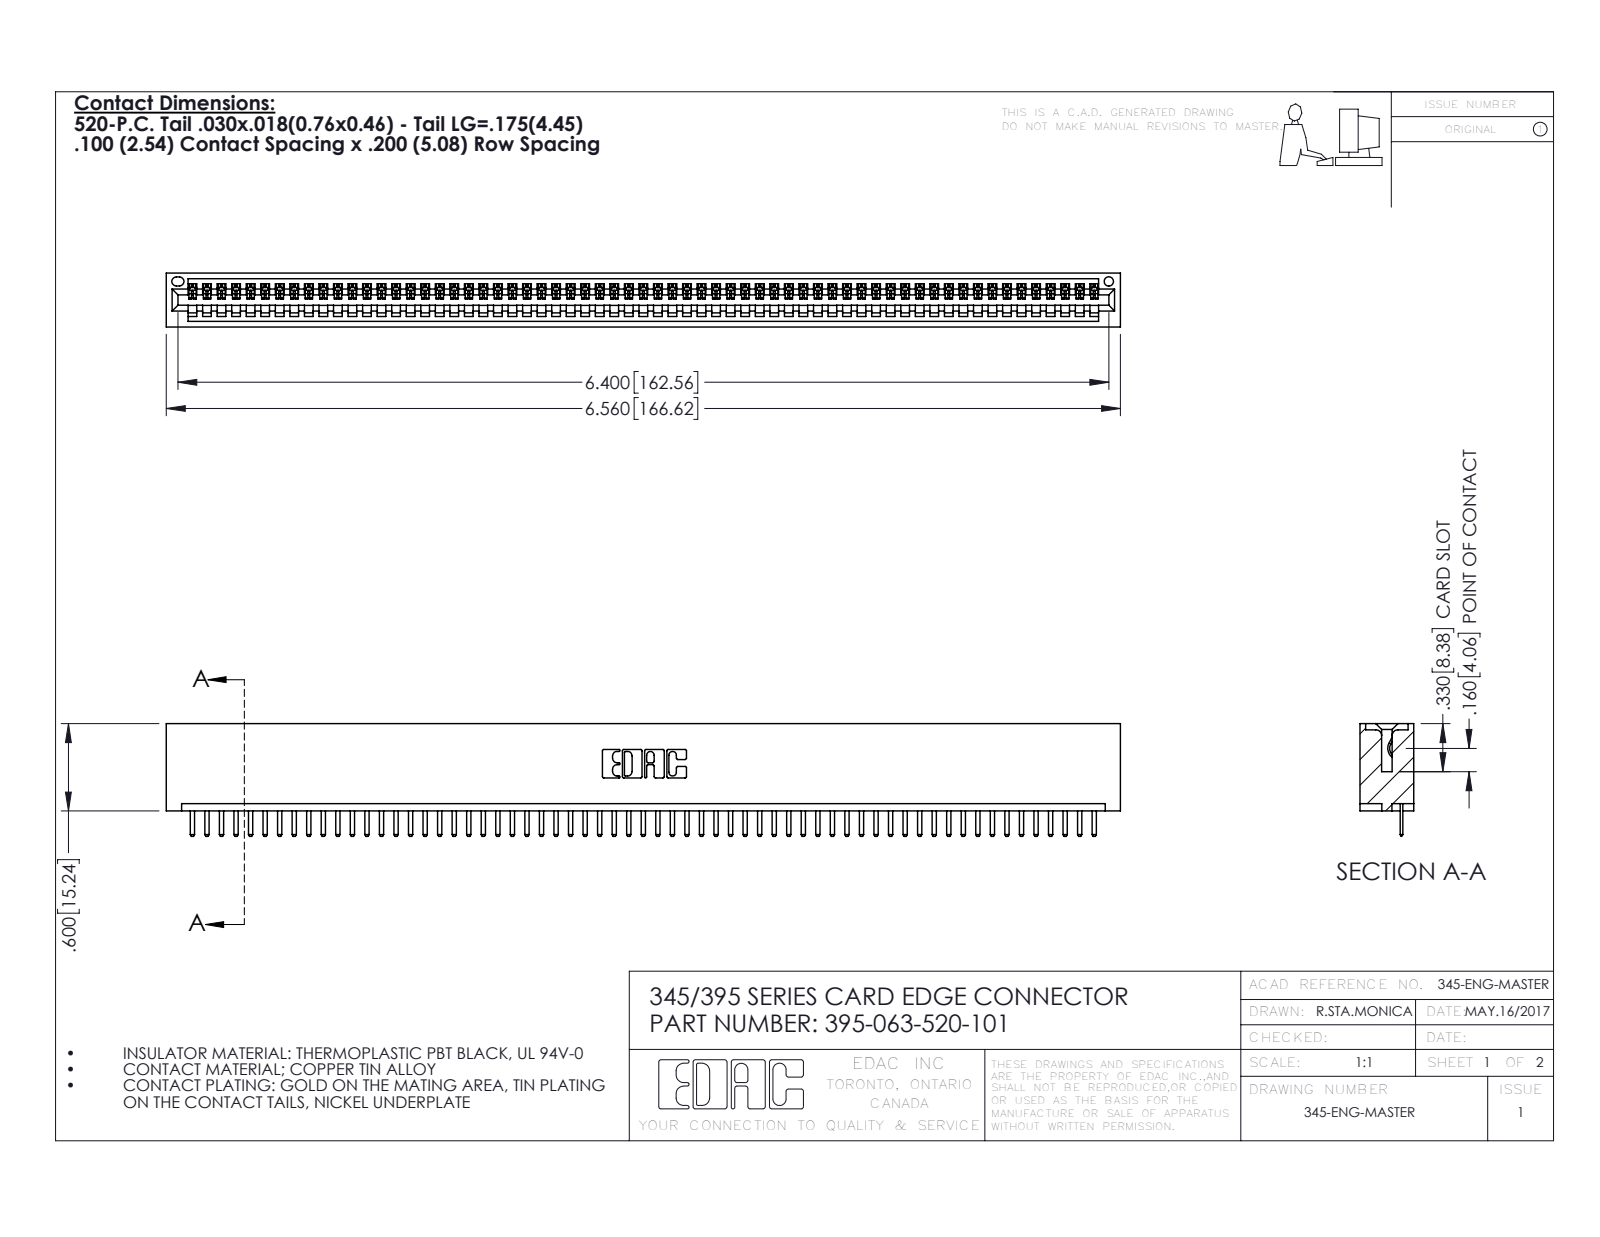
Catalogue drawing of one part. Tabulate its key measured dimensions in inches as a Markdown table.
| quantity | value |
| --- | --- |
| part name | 345 Part_No Mounting Lugs; 395-063-520-101; 345-292-001_345-293-120 |
| STEP written by | SolidWorks 2016 (CONFIG_CONTROL_DESIGN) |
| units | inches |
| bodies | 64 solids, 4024 faces (2722 planar, 1302 cylindrical, 0 other) |
| overall size | 6.56 × 0.775 × 0.37 |
| volume | 1.001 in³ |
| surface area | 33.6 in² |
| round holes (diameter × count) | 0.064 × 1 |
| partial cylindrical surfaces (radius × count) | 0.01 × 128, 0.006 × 126, 0.01 × 22, 0.007 × 6, 0.031 × 6, 0.026 × 3, 0.031 × 2, 0.04 × 2 |
| main face-to-face distances | 0.298, 0.072, 0.37, 0.2, 0.098, 0.272, 0.025, 0.225, 0.072, 0.149 |
